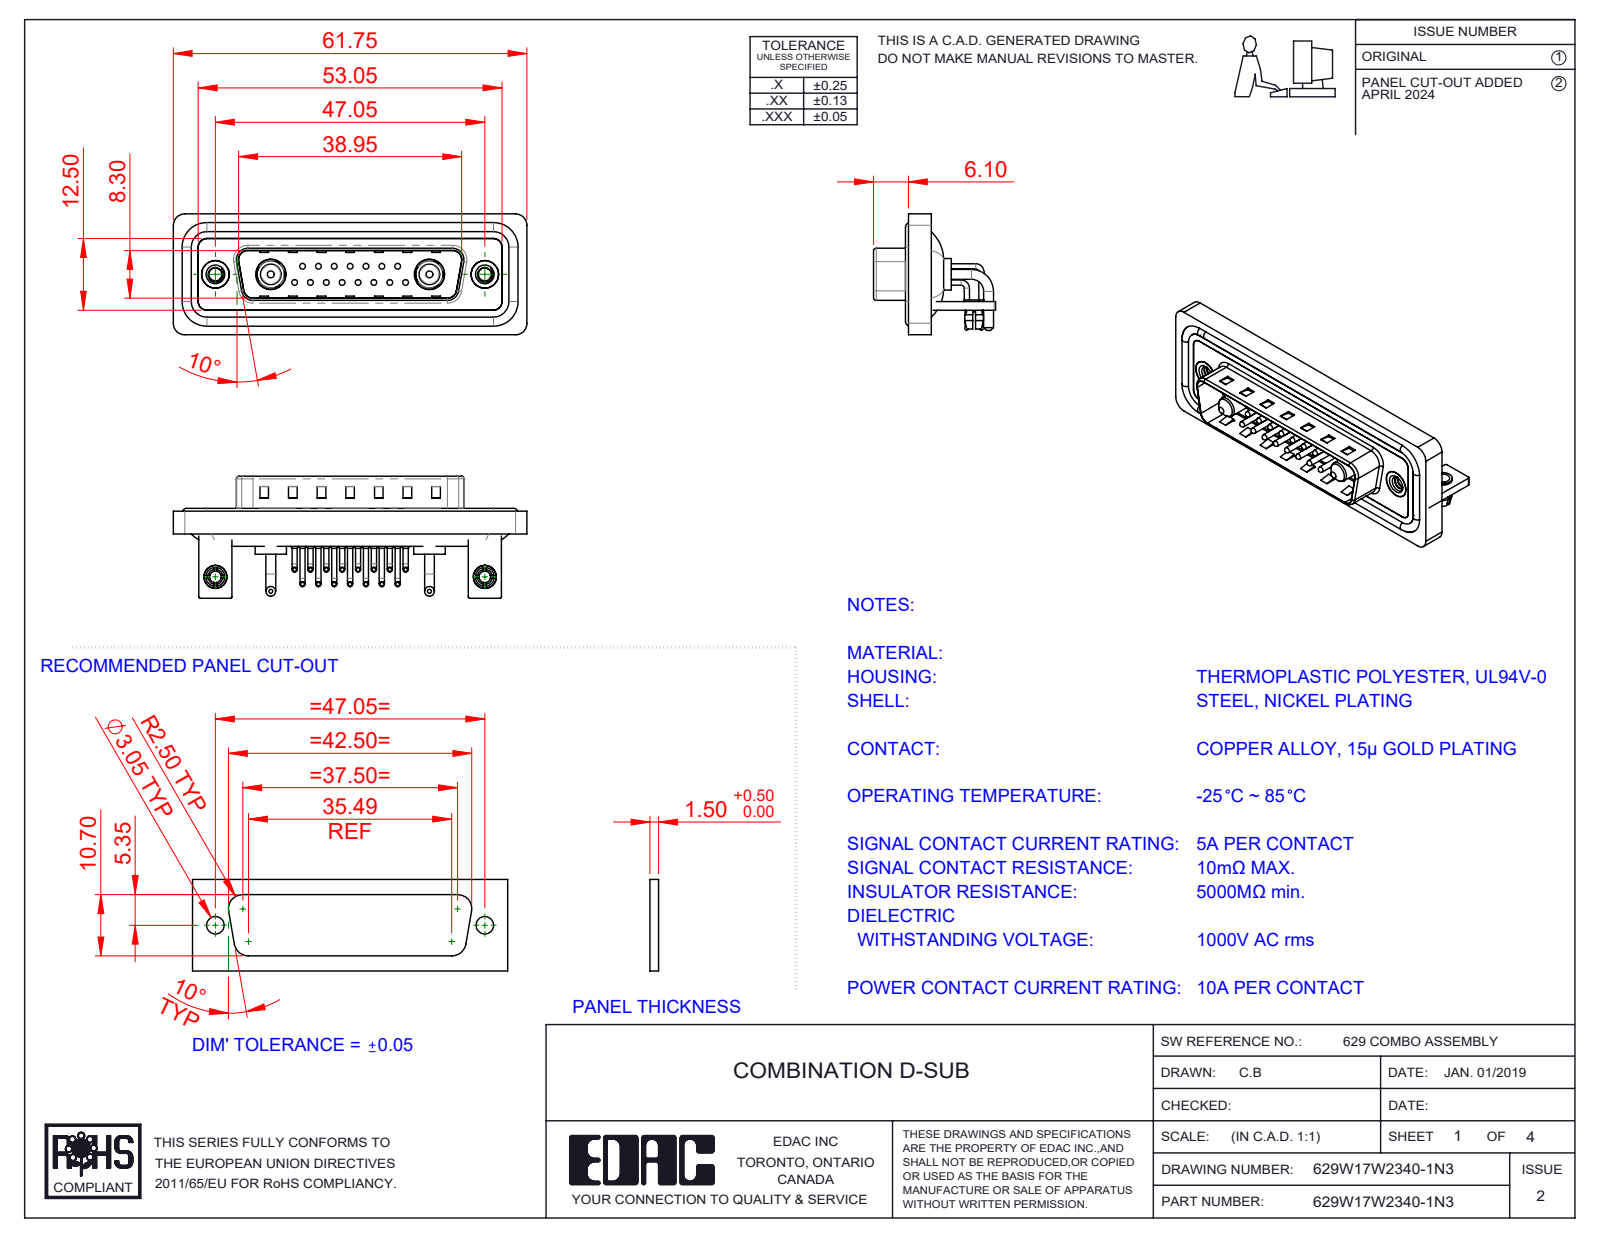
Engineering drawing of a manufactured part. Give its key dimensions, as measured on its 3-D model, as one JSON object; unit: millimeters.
{"part_name": "Power Pin_10A RA; 629Combo Waterproof Housing_25 Contacts; 629Combo Shell Front_25 Contacts; 629Combo Contact Row 2 (+7 more)", "step_written_by": "SolidWorks 2023 (CONFIG_CONTROL_DESIGN)", "units": "millimeters", "bodies": {"solids": 30, "faces": 2351, "planar": 1257, "cylindrical": 820, "other": 274}, "overall_size": [61.75, 21.3, 21.1], "volume_mm3": 7710, "surface_area_mm2": 13296, "round_holes": [[2, 17], [0.75, 15], [1.6, 15], [2.26, 2], [2.5, 2], [3.2, 2], [4, 2], [4.8, 2], [4.85, 2], [5, 2], [5.3, 2]], "round_bosses_or_shafts": [[0.9, 30], [1.5, 15], [1, 15], [0.65, 15], [1.7, 4], [1.6, 4], [5.5, 2], [5.2, 2]], "partial_cylinders_radius": [[2, 19], [1.5, 18], [0.25, 16], [1.01, 15], [0.5, 9], [1.6, 8], [0.6, 4], [0.65, 4]], "face_to_face_distances": [0.4, 0.8, 1.5, 2.1, 2.9, 1.1, 4.1, 1.6, 4.5, 3.7], "hole_center_spacings": [3.16, 2.77, 5.54, 8.31, 5.04, 7.49, 11.08, 5.03]}
